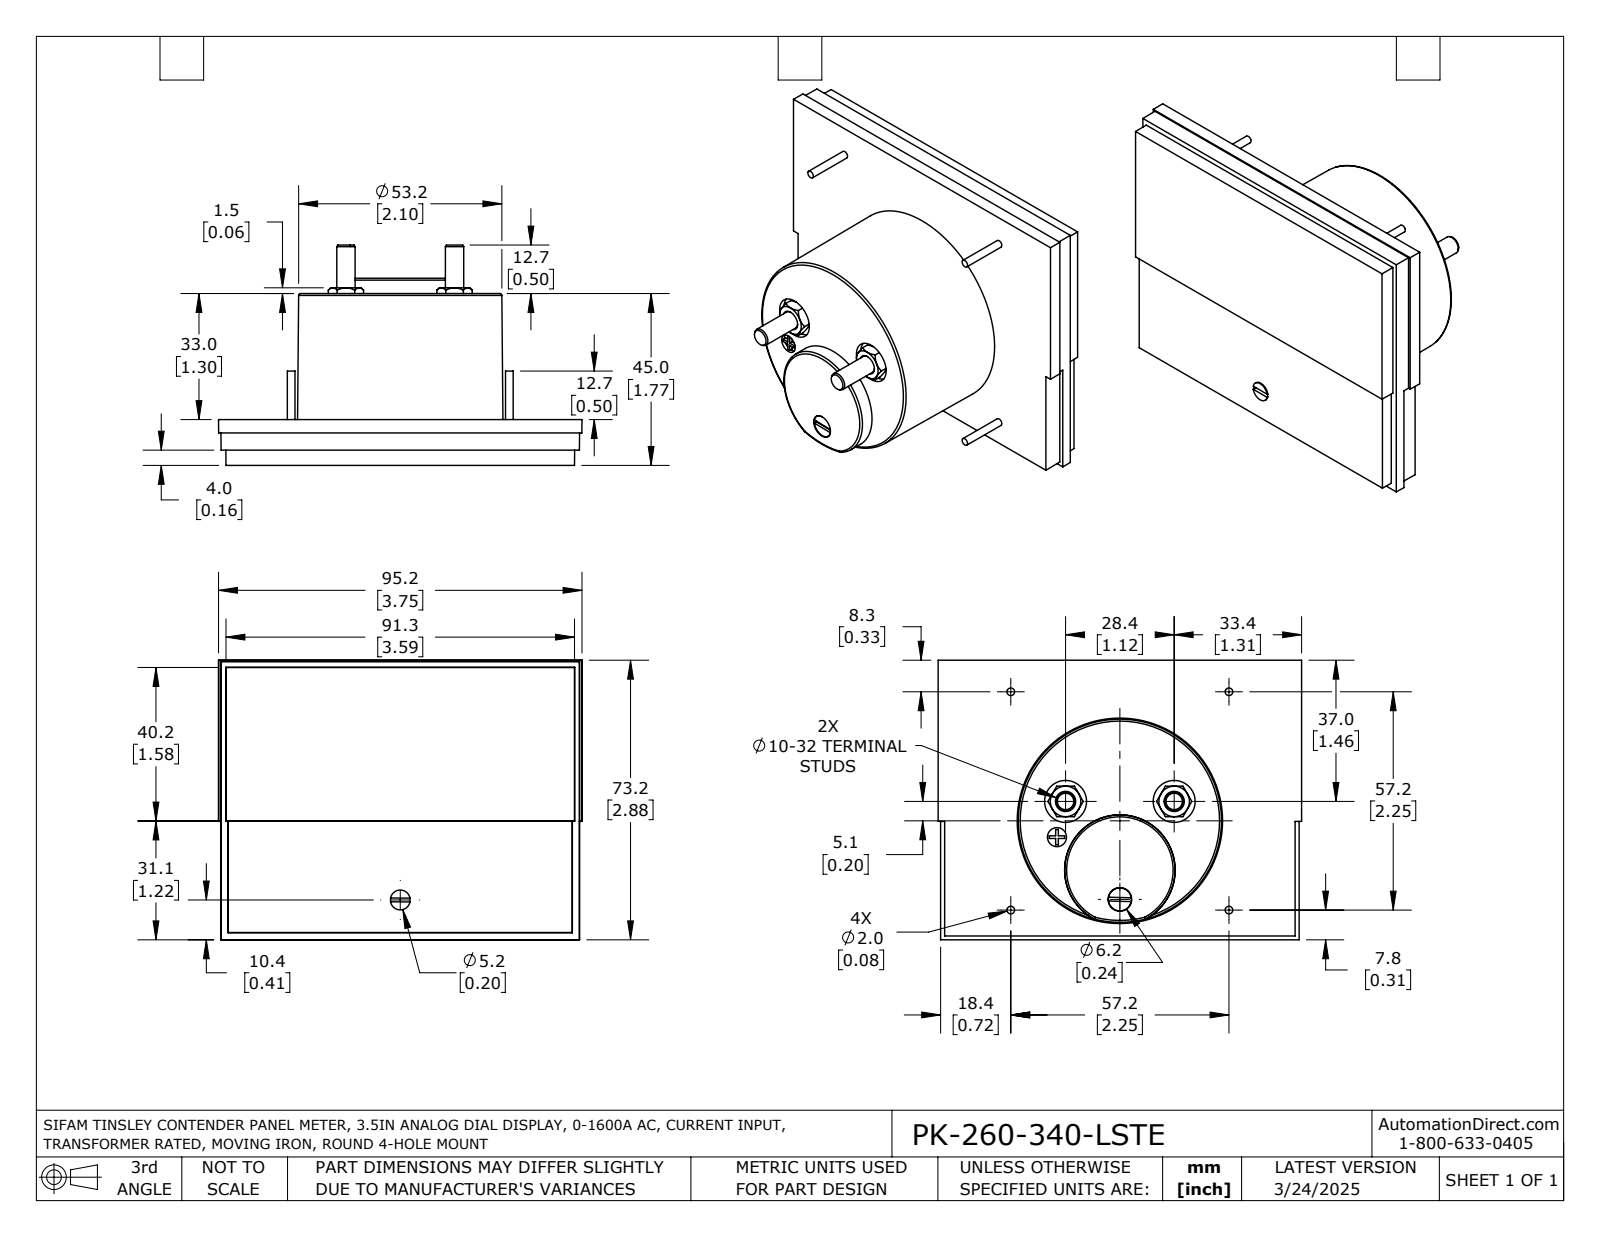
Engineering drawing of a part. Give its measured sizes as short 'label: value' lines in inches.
name: PK-260-340-LSTE
written by: SolidWorks 2021 (AUTOMOTIVE_DESIGN)
unit: in
bodies: 1 solid, 163 faces (76 planar, 31 cylindrical, 56 other)
size: 3.748 × 2.882 × 2.272
volume: 9.446 in³; area: 38.39 in²
holes: 2× ⌀0.433, 1× ⌀0.197, 1× ⌀0.244
bosses: 4× ⌀0.079, 2× ⌀0.189, 1× ⌀0.236, 1× ⌀0.205
rounds: 1× R0.1
face distances: 0.472, 0.03, 0.443, 1.772, 1.299, 1.742, 0.157, 0.073, 0.315, 1.457
hole spacings: 1.155, 0.379, 0.912, 1.12, 1.263
